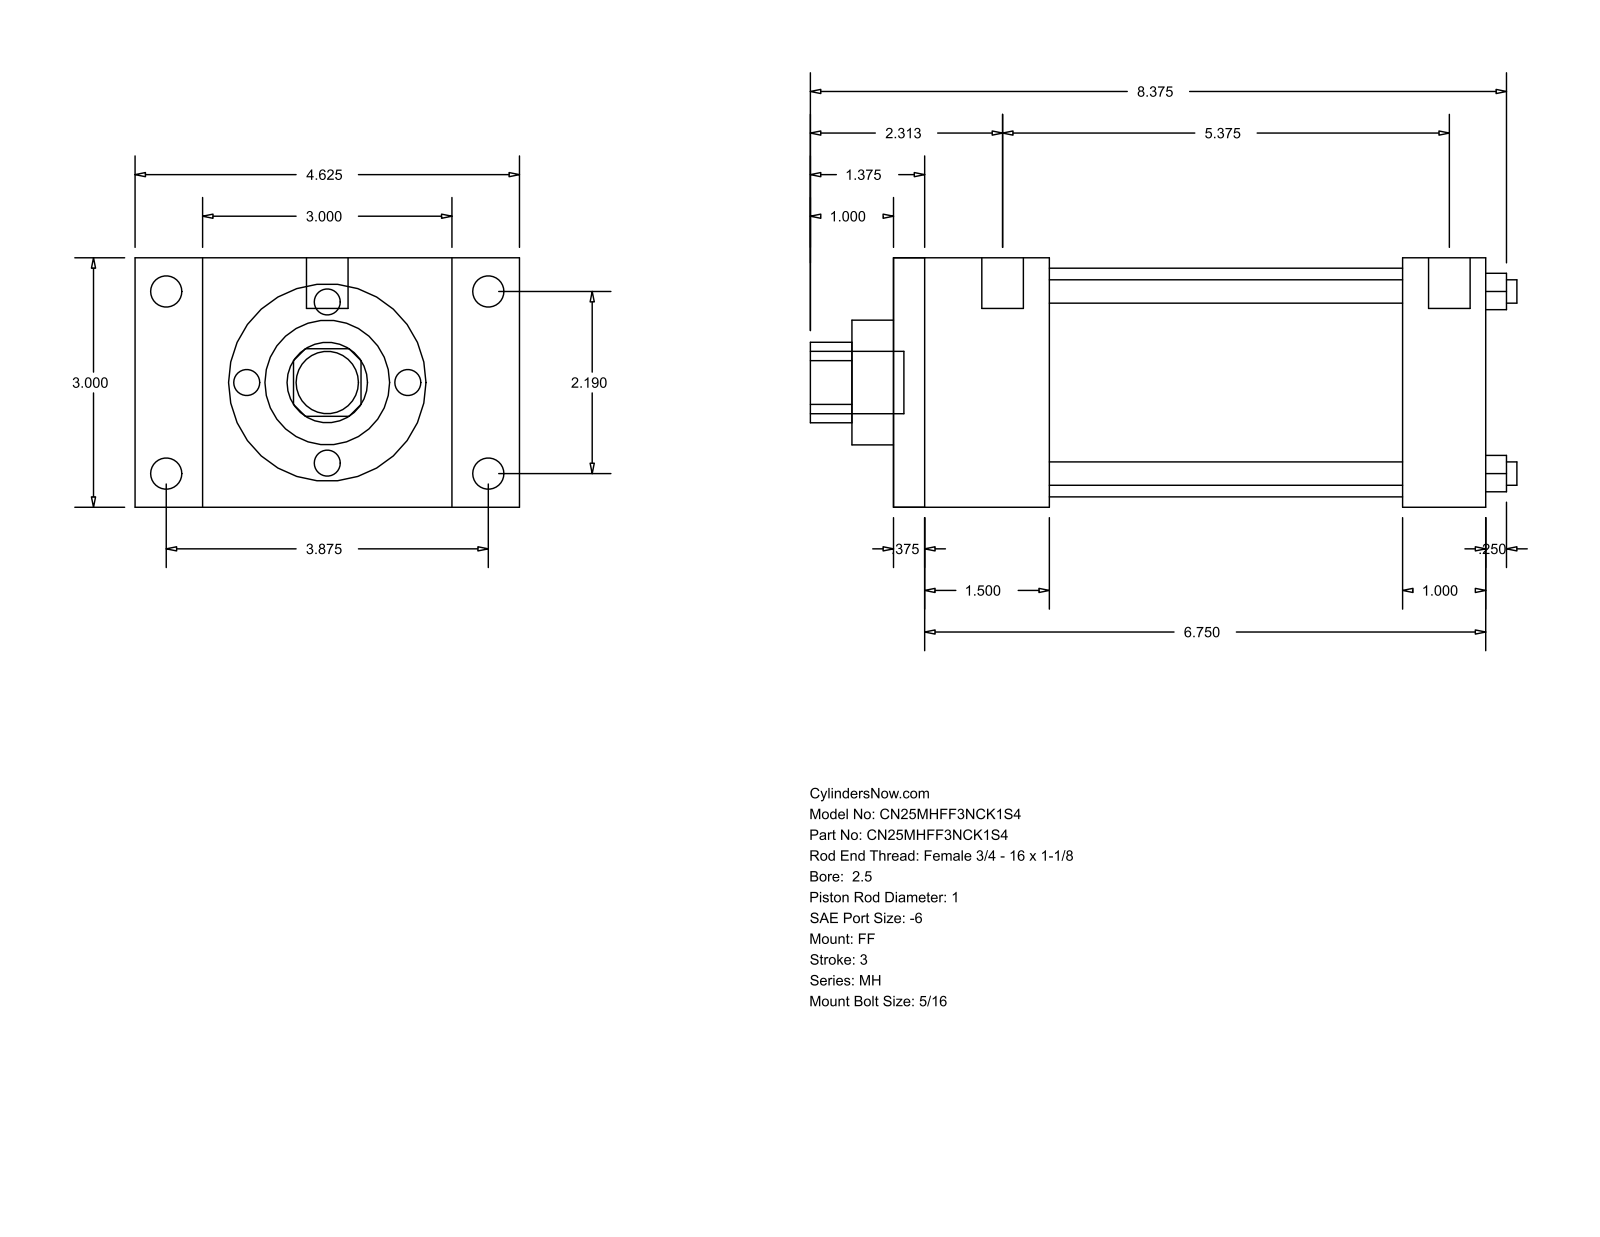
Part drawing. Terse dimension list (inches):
name: MH_FF__0250_1
written by: GSSL Pune (CONFIG_CONTROL_DESIGN)
unit: in
bodies: 0 solids, 92 faces (64 planar, 28 cylindrical, 0 other)
size: 8.5 × 4.625 × 3
holes: 4× ⌀0.281, 1× ⌀1, 1× ⌀1.5, 1× ⌀2.75
bosses: 4× ⌀0.375, 4× ⌀0.219, 2× ⌀0.5, 1× ⌀0.75
rounds: 1× R0.484
face distances: 3, 7.125, 0.375, 6.75, 1.875, 6.125, 1.5, 5.75, 4.25, 5.25
hole spacings: 1.548, 2.19, 3.097
